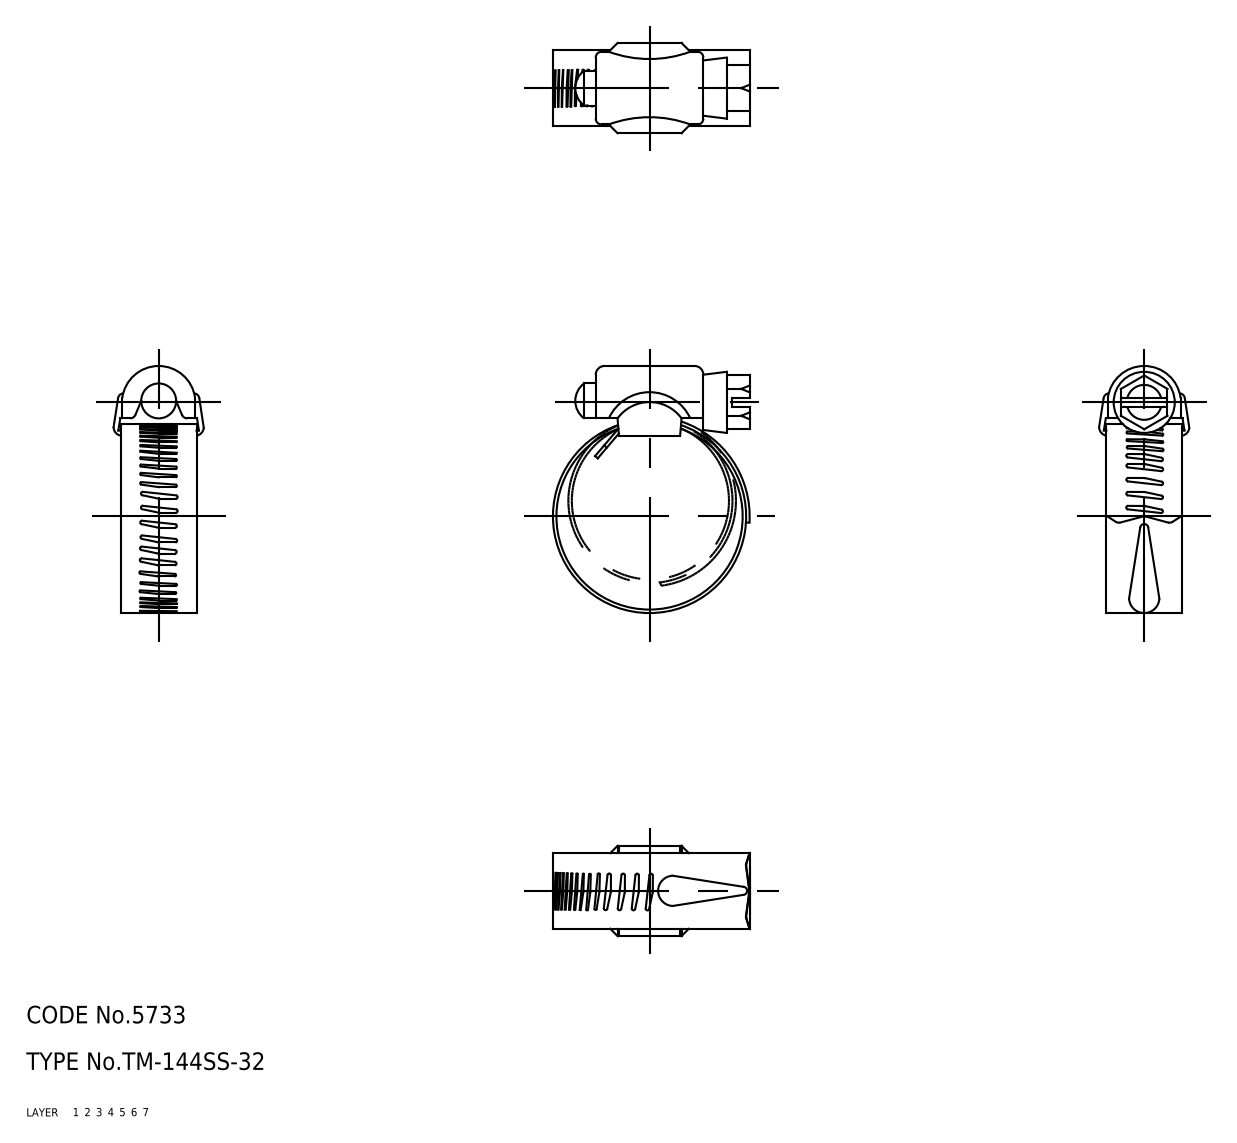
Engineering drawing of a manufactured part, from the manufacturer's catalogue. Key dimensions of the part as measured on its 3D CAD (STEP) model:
Part name (STEP PRODUCT): screw; holder; band; TM_144SS_32_19809_36
STEP written by: CADfix (AUTOMOTIVE_DESIGN)
Units: millimetres
Bodies: 3 solids, 206 faces (0 planar, 0 cylindrical, 206 other)
Overall size (bounding box): 42.45 × 33.85 × 15.63
Volume: 3 210 mm³ · Surface area: 5 970 mm²
